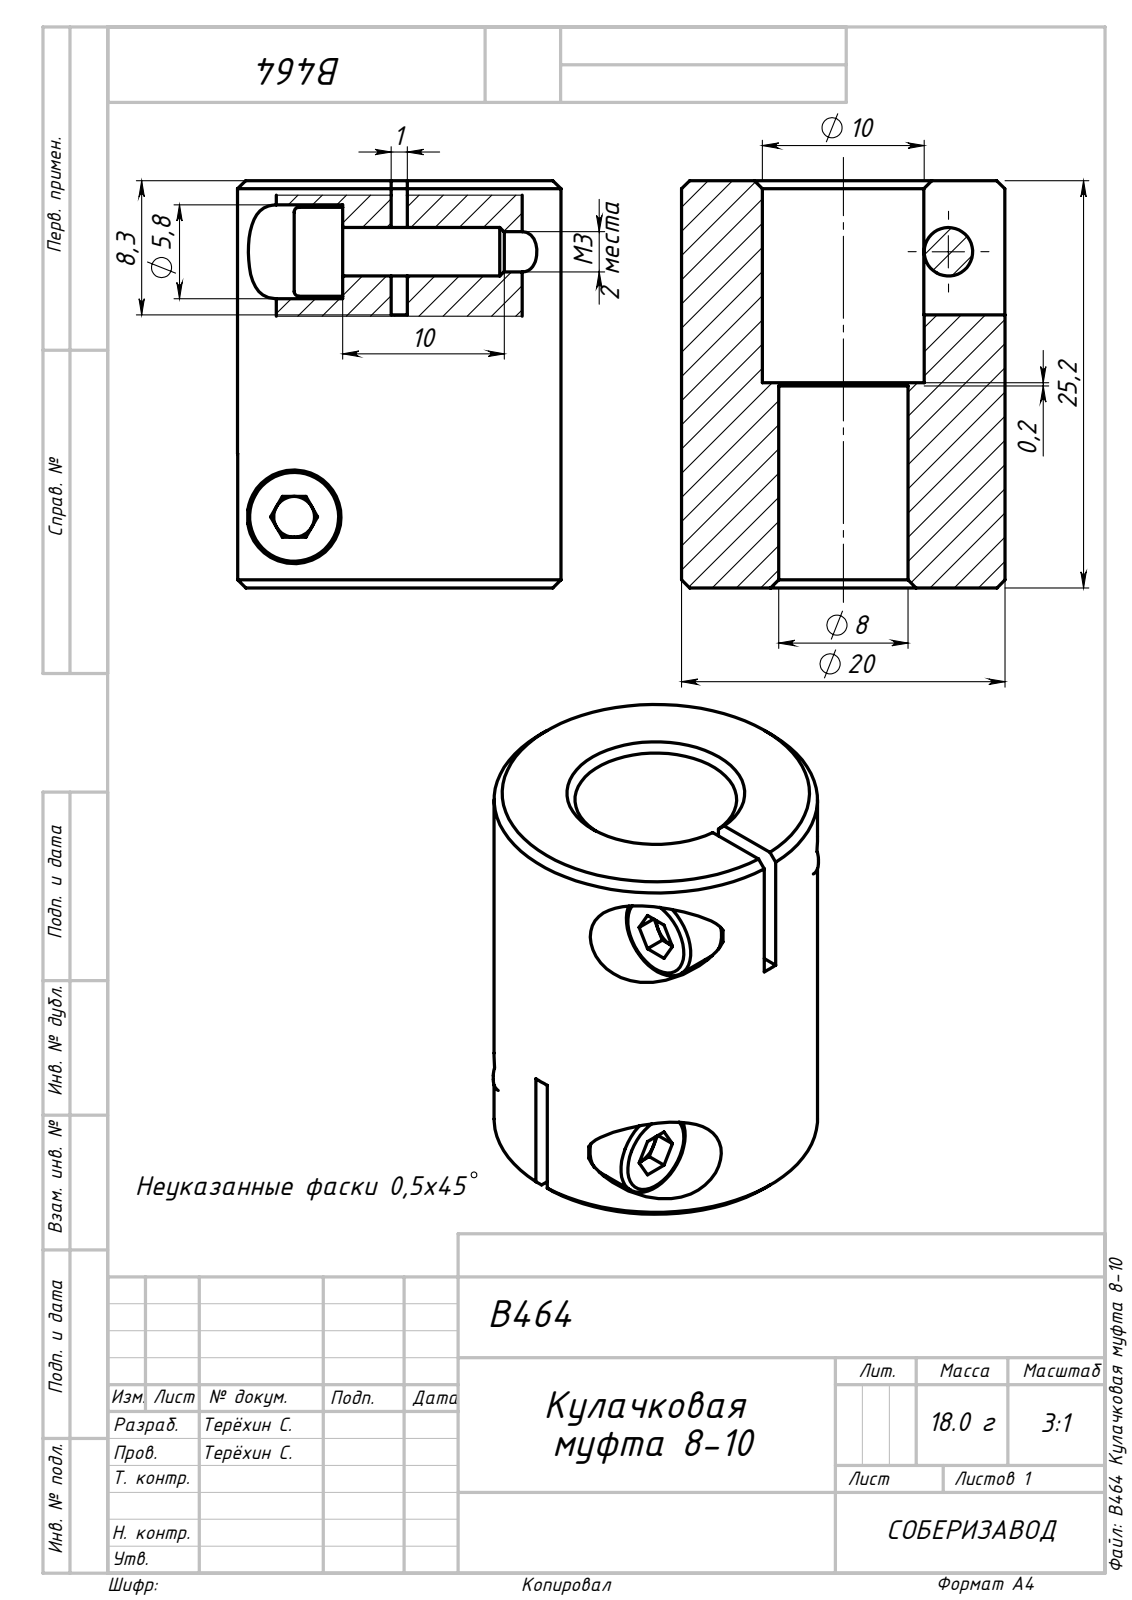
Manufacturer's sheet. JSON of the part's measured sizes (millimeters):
{"part_name": "B464 Кулачковая муфта 8-10_00; Винт M3x10_00; Сборка1", "step_written_by": "SolidWorks 2022 (AUTOMOTIVE_DESIGN)", "units": "millimeters", "bodies": {"solids": 3, "faces": 95, "planar": 42, "cylindrical": 28, "other": 25}, "overall_size": [25.2, 20, 20], "volume_mm3": 6158, "surface_area_mm2": 3639, "round_holes": [[2.5, 2], [5.8, 2], [8, 1], [10, 1]], "round_bosses_or_shafts": [[5.5, 2], [3, 2], [20, 1]], "face_to_face_distances": [25.2, 12.5, 12.7, 3, 1, 4, 6, 7, 2.52, 8.3]}
